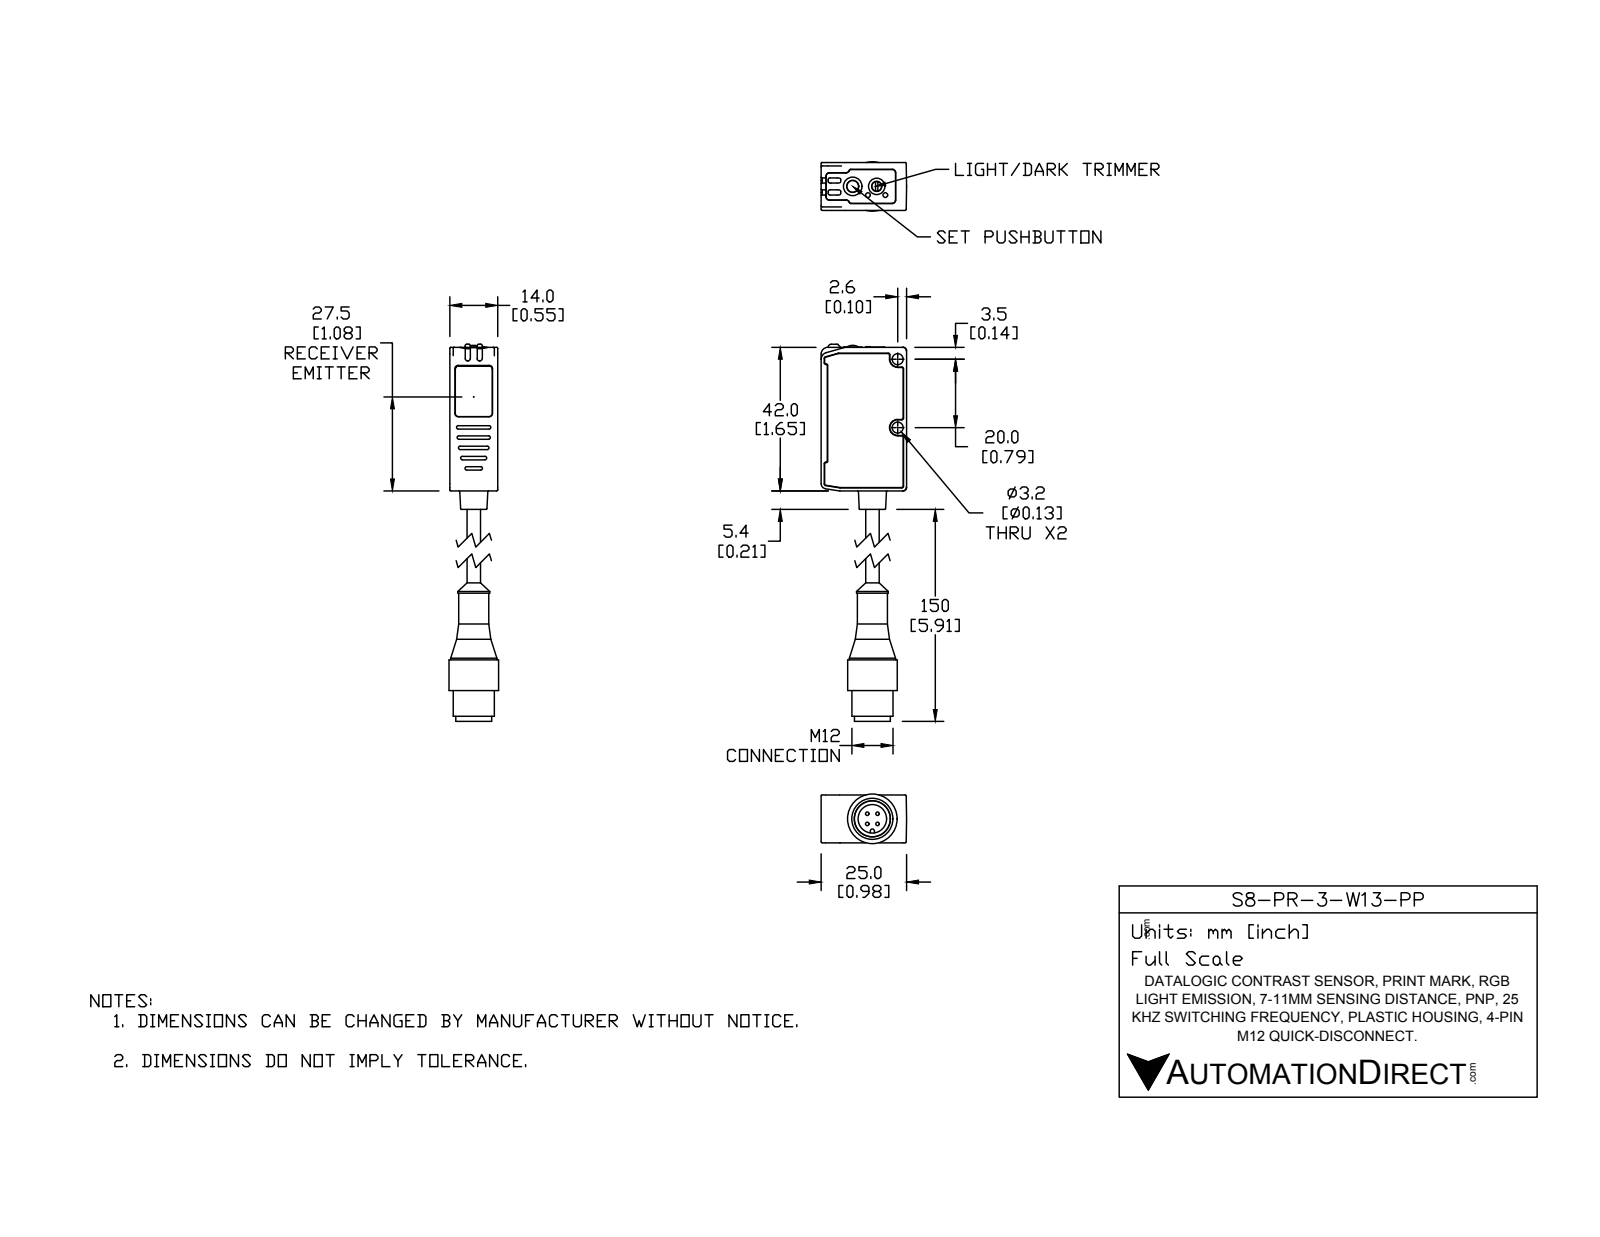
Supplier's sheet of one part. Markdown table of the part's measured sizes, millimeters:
| quantity | value |
| --- | --- |
| part name | S8-PR-3-W13-PP |
| STEP written by | SolidWorks 2016 (AUTOMOTIVE_DESIGN) |
| units | millimeters |
| bodies | 13 solids, 453 faces (132 planar, 203 cylindrical, 118 other) |
| overall size | 198.3 × 25 × 14.5 |
| volume | 18 834 mm³ |
| surface area | 10 015 mm² |
| round holes (diameter × count) | 3.2 × 2, 1.4 × 1, 2.95 × 1, 3.5 × 1, 8.3 × 1, 10.55 × 1 |
| round bosses / shafts (diameter × count) | 1 × 4, 14.5 × 1, 13.5 × 1, 12 × 1, 10.5 × 1, 9.3 × 1, 8.8 × 1, 3.95 × 1 |
| partial cylindrical surfaces (radius × count) | 0.2 × 41, 0.5 × 32, 0.3 × 18, 1 × 14, 0.4 × 13, 0.7 × 4, 0.95 × 4, 2 × 3 |
| main face-to-face distances | 14, 0.6, 178.8, 179.4, 137.4, 41.4, 42, 0.8, 1, 9 |
| hole center spacings | 1.25, 3.61, 4.58, 5.75, 7, 9.88, 20 |
